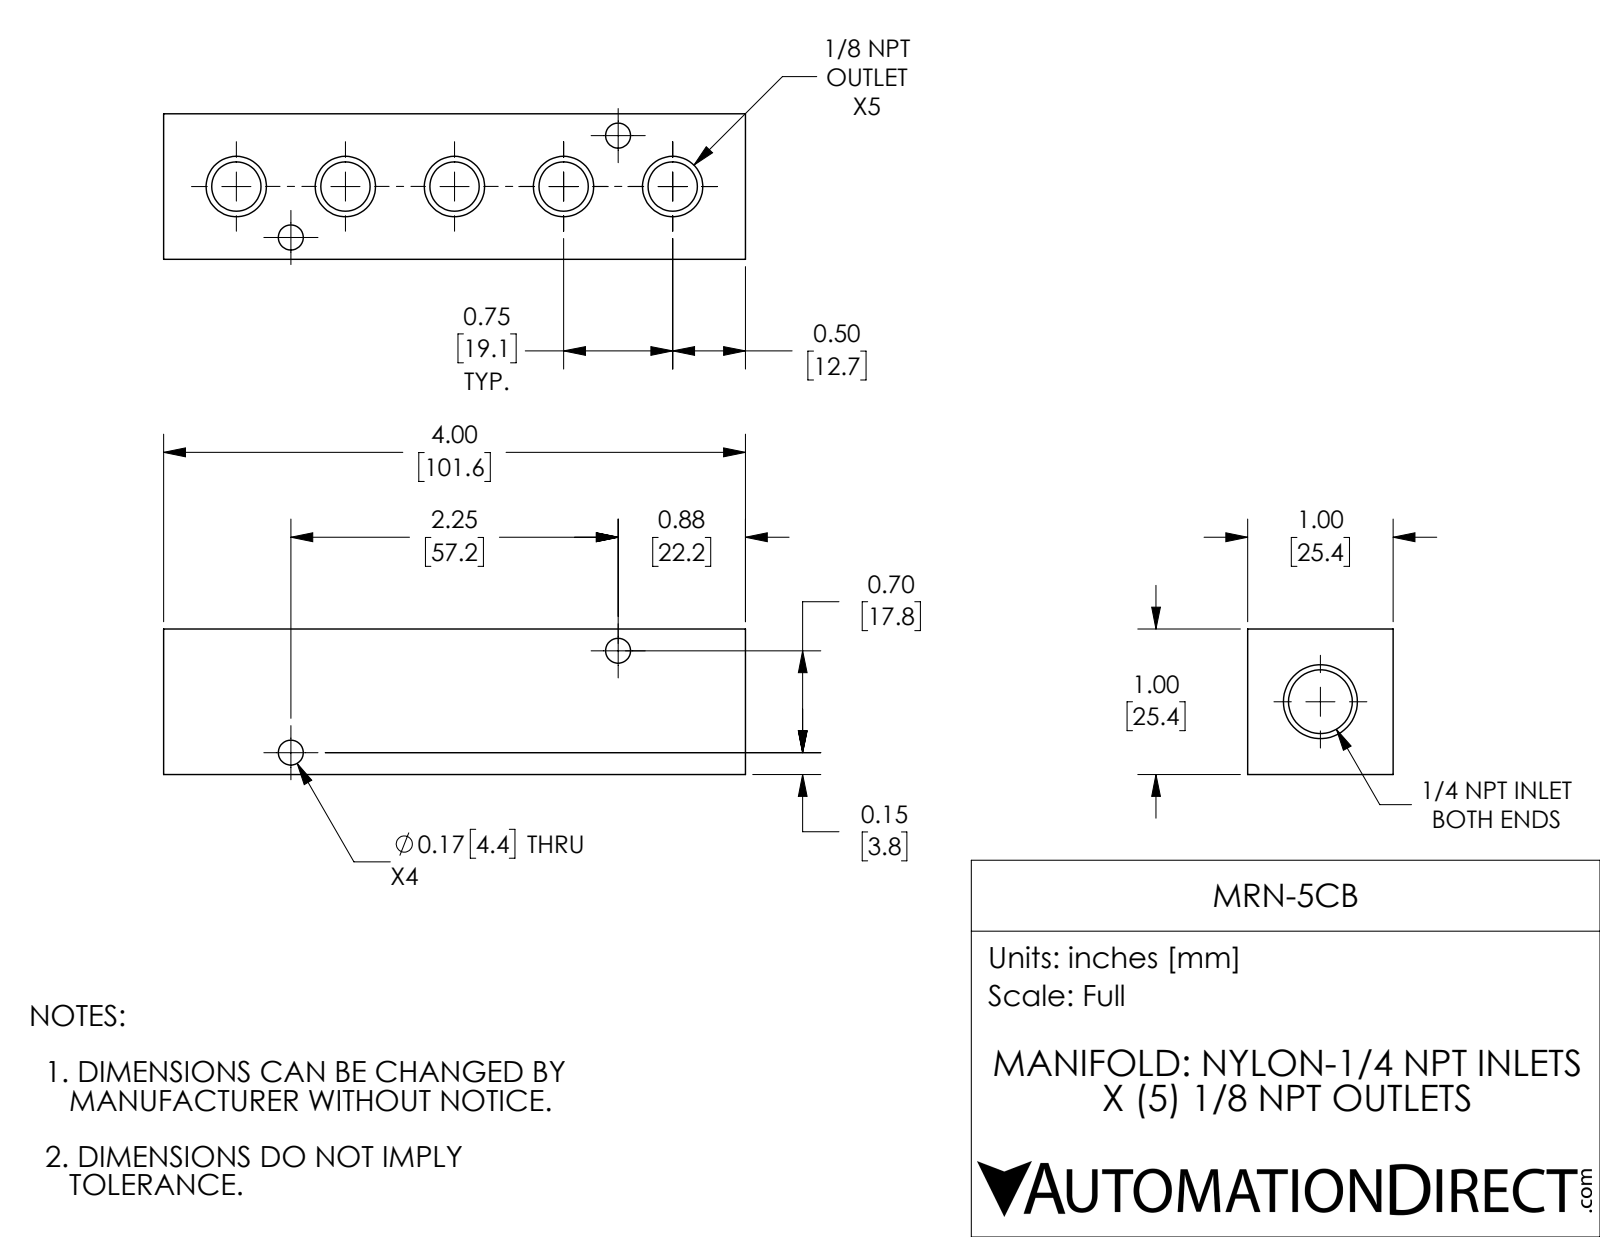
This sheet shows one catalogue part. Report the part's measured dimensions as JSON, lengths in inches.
{"part_name": "MRN-5CB", "step_written_by": "SolidWorks 2018 (AUTOMOTIVE_DESIGN)", "units": "inches", "bodies": {"solids": 1, "faces": 48, "planar": 6, "cylindrical": 28, "other": 14}, "overall_size": [4, 1, 1], "volume_in3": 3.17, "surface_area_in2": 25.53, "round_holes": [[0.339, 5], [0.172, 4], [0.438, 1]], "face_to_face_distances": [1, 4], "hole_center_spacings": [0.513, 0.75, 1.5, 1.178, 1.907, 2.25, 2.357, 2.648]}
